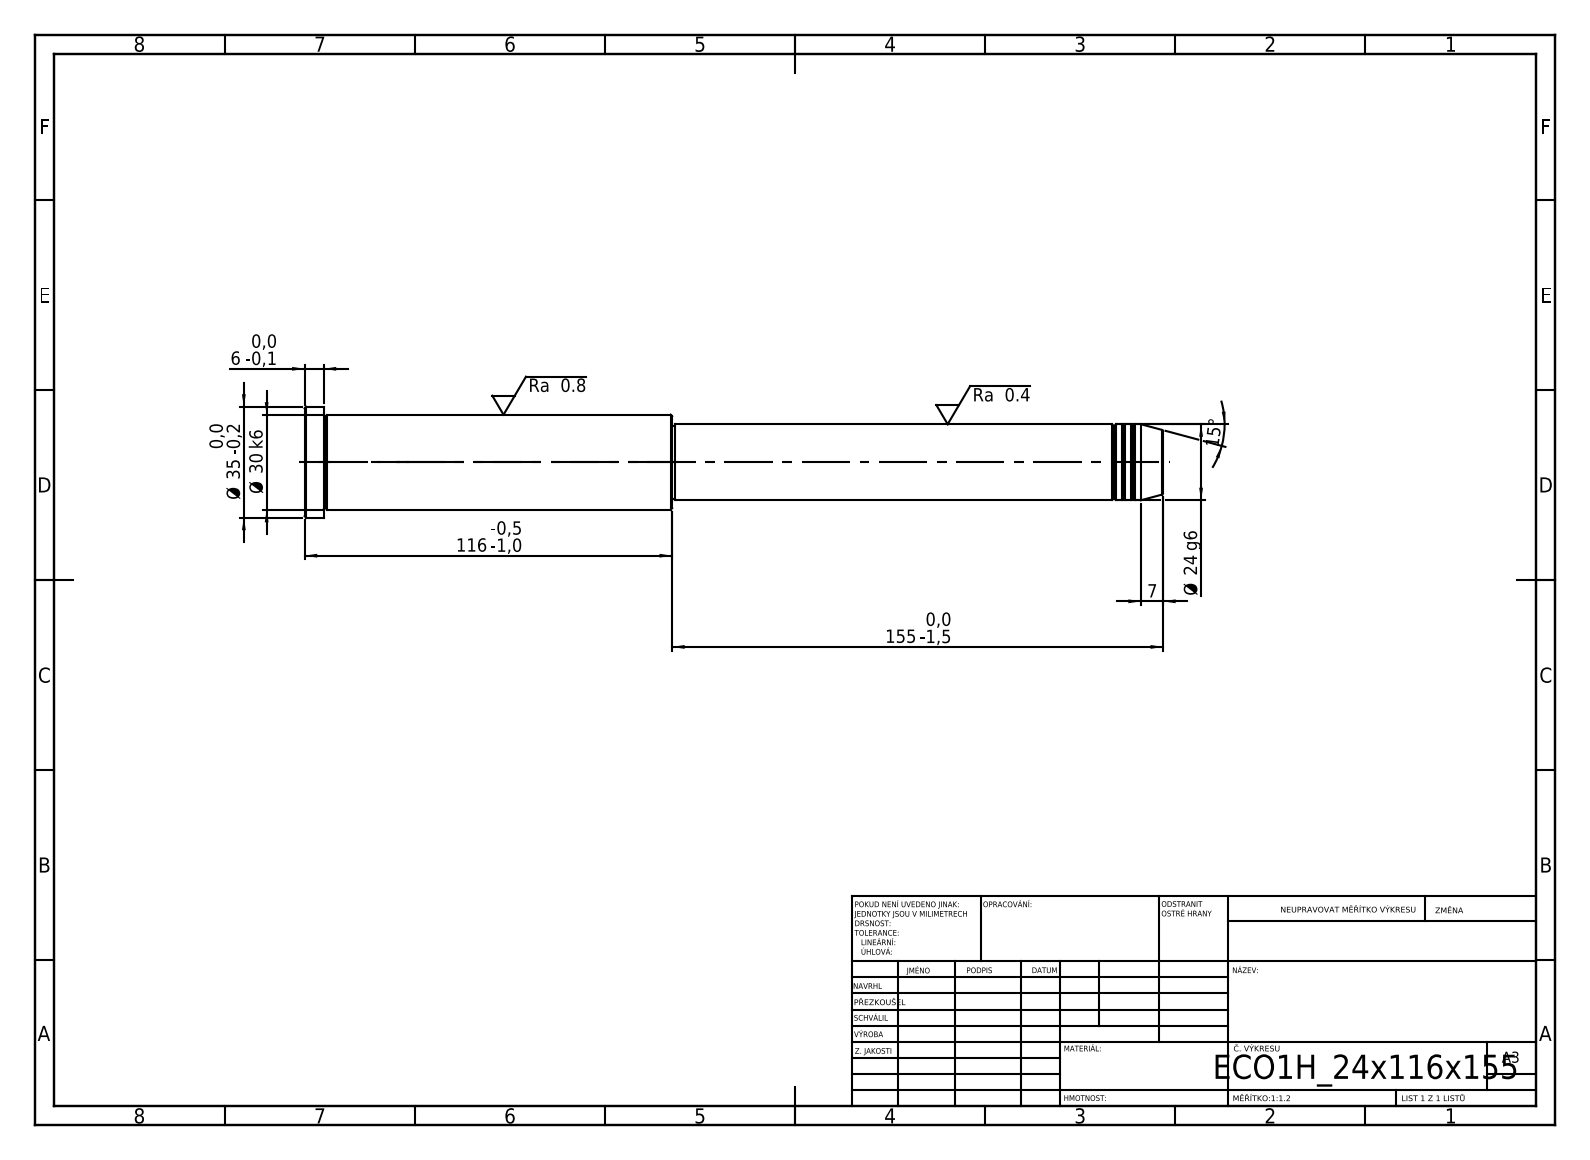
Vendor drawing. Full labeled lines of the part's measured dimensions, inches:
STEP written by: SolidWorks 2019 (CONFIG_CONTROL_DESIGN)
Units: inches
Bodies: 1 solid, 43 faces (5 planar, 14 cylindrical, 24 other)
Overall size (bounding box): 10.669 × 1.378 × 1.378
Volume: 9.336 in³ · Surface area: 38.22 in²
Round bosses / shafts (diameter × count): ⌀1.378 ×1, ⌀1.181 ×1, ⌀0.945 ×1, ⌀0.906 ×1
Main face-to-face distances: 10.669, 10.433, 0.236, 6.102, 4.331, 4.567, 6.063, 0.039, 4.37, 4.606
